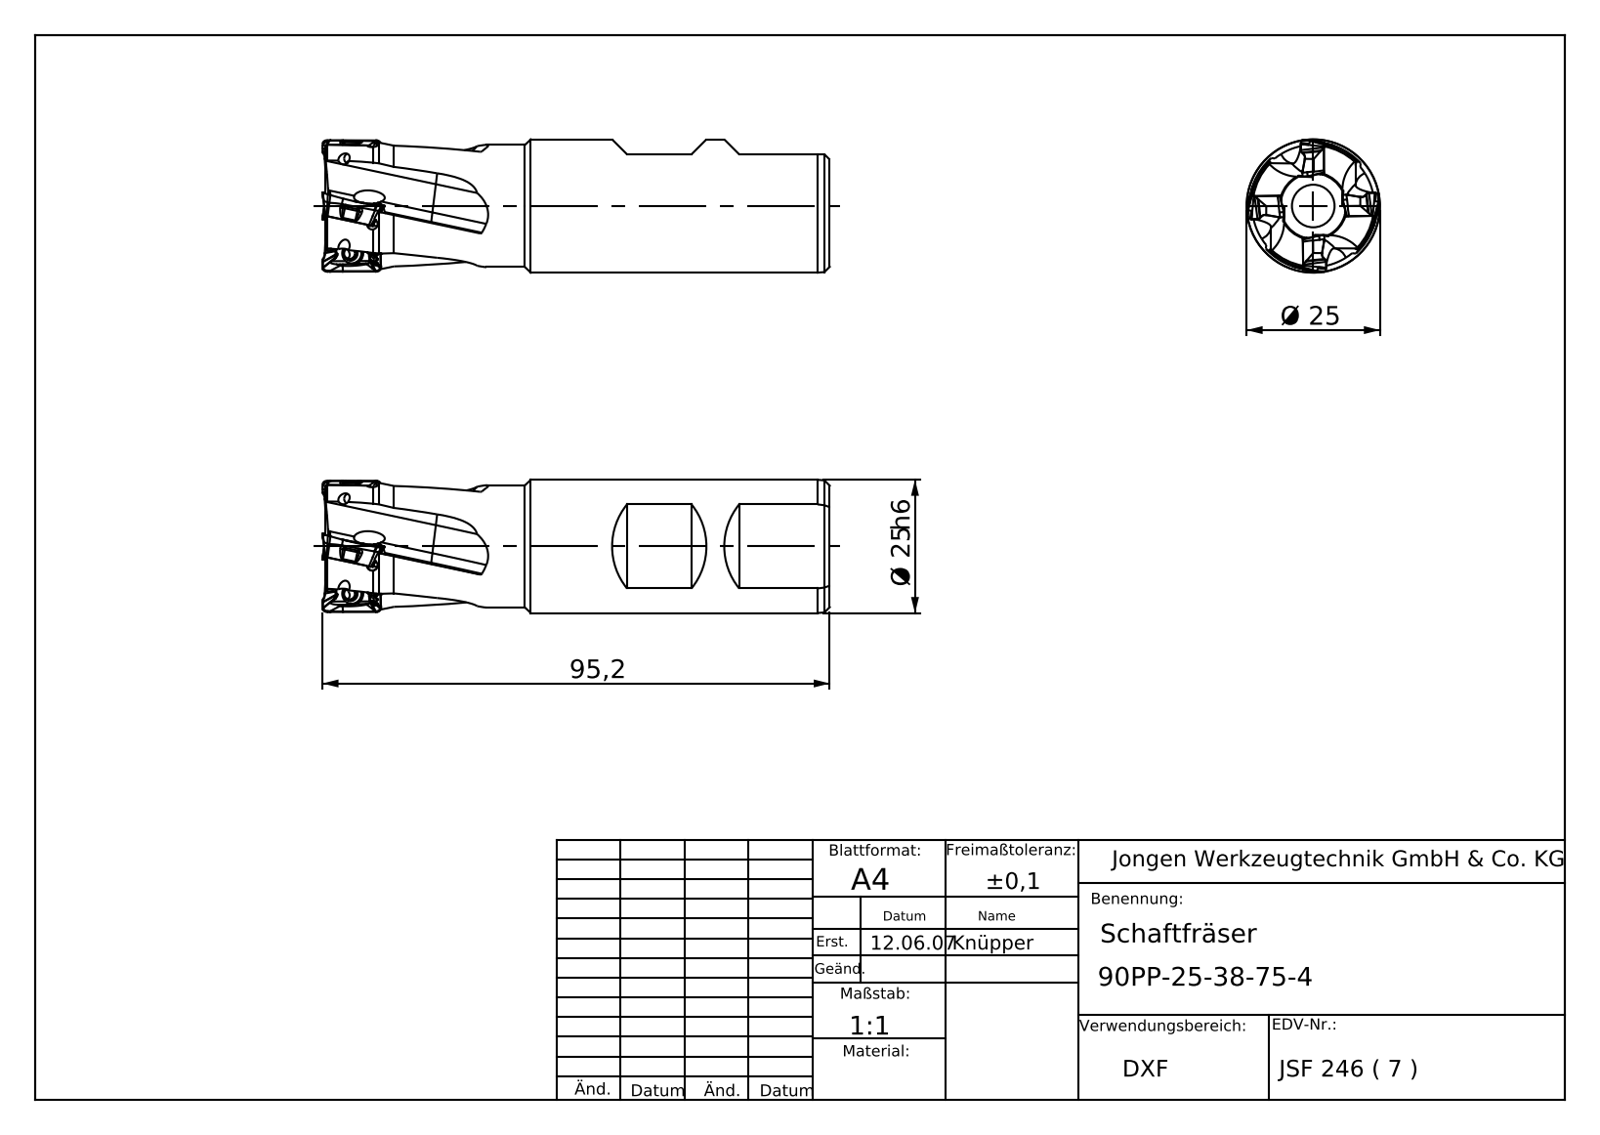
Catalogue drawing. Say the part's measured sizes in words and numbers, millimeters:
The part is named "90PP-25-38-75-4". Its 3-D file was written by "SolidWorks 2012 (AUTOMOTIVE_DESIGN)". It is 1 solid with 166 faces: 60 planar, 46 cylindrical and 60 other. Overall it measures 95.2 by 25 by 25 millimeters. Its volume is 37 293 cubic millimeters and its surface area 11 310 square millimeters. Round holes: 4 of diameter 2.5, 1 of diameter 6.5. Round bosses or shafts: 1 of diameter 25, 1 of diameter 22.94. Partial cylindrical surfaces (rounded edges, fillets, slot ends): 12 of radius 1.5, 4 of radius 0.2, 1 of radius 6.15, 1 of radius 11.97. The main face-to-face distances are 93.22, 14.89, 10.92, 0.5, 11.31, 26.2, 11.42, 2.81, 5, 11.92.
